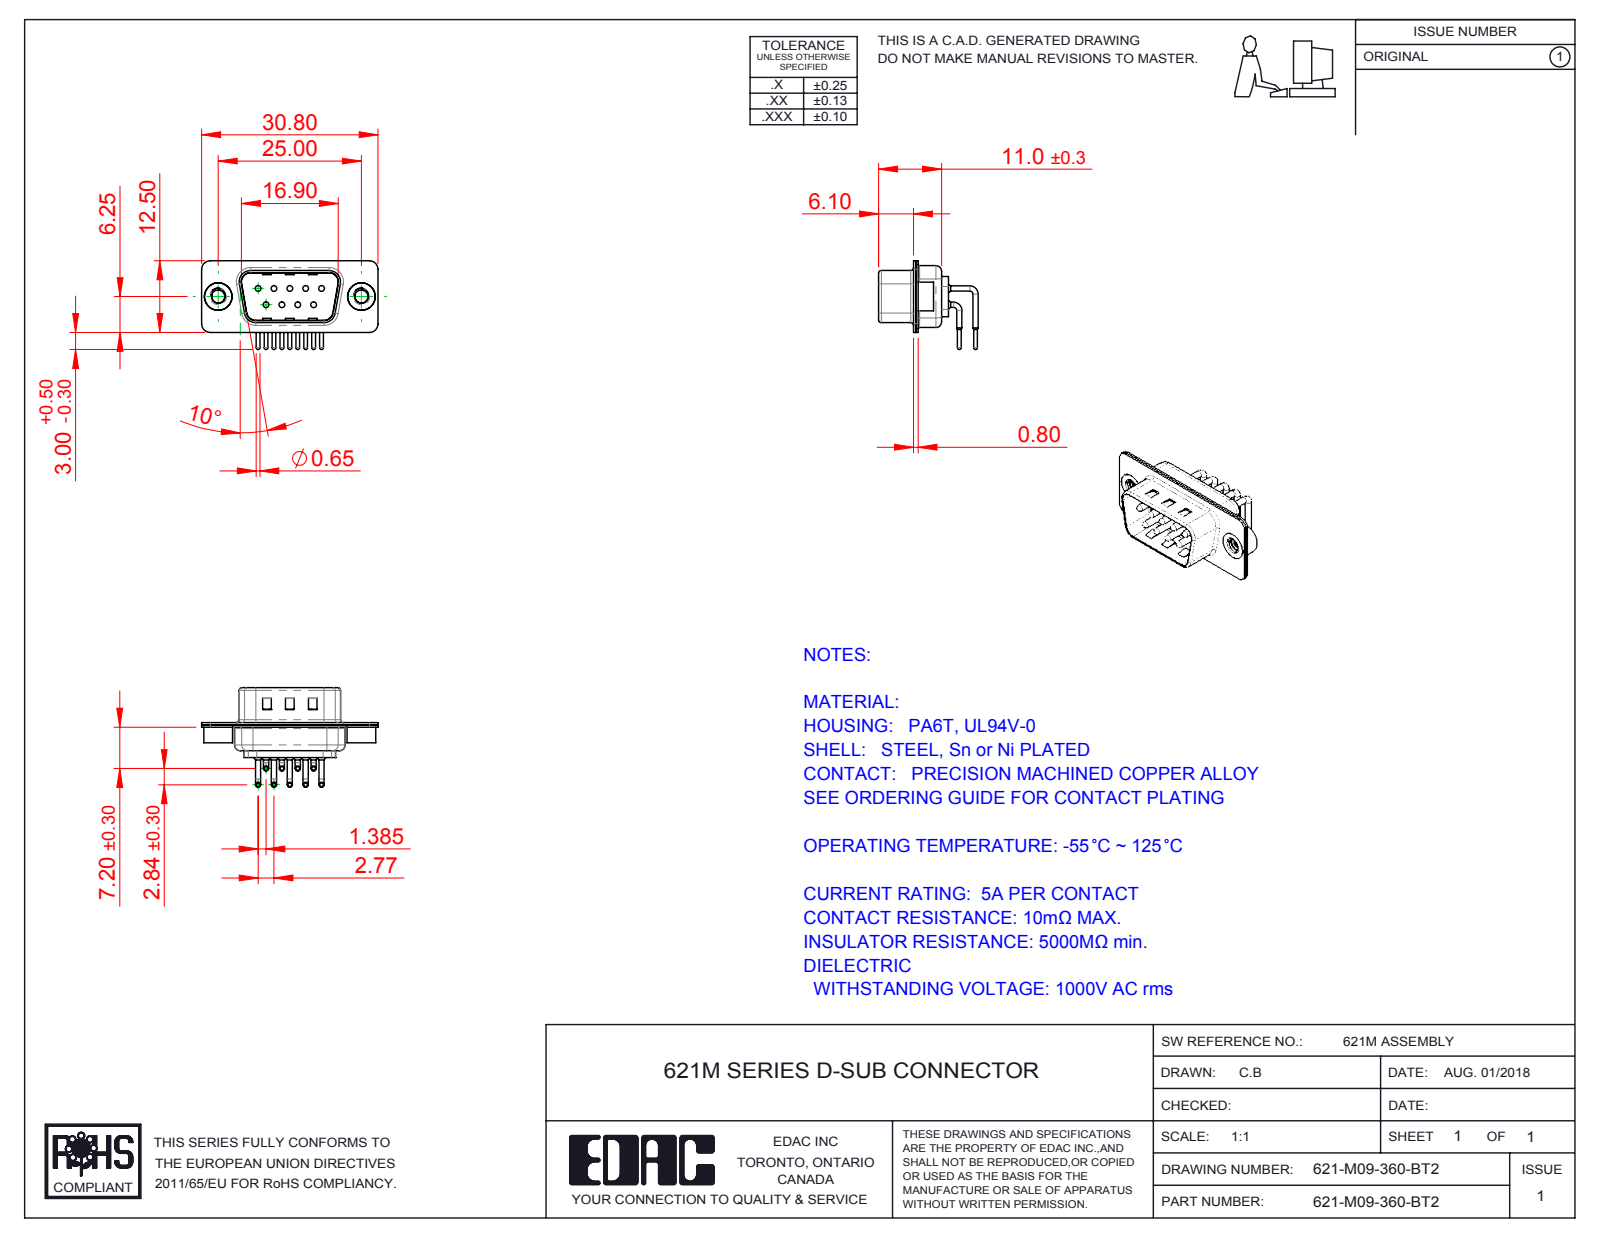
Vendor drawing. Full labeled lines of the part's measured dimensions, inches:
Part name (STEP PRODUCT): 621M Shell Front_09 Contacts; 621M Housing_09 Contacts; 621M Contact Row 2; 621M Shell Rear_09 Contacts (+3 more)
STEP written by: SolidWorks 2016 (CONFIG_CONTROL_DESIGN)
Units: inches
Bodies: 14 solids, 1294 faces (683 planar, 453 cylindrical, 158 other)
Overall size (bounding box): 1.213 × 0.685 × 0.61
Volume: 0.083 in³ · Surface area: 5.969 in²
Round holes (diameter × count): ⌀0.039 ×9, ⌀0.067 ×9, ⌀0.079 ×9, ⌀0.089 ×2, ⌀0.157 ×2, ⌀0.189 ×2
Round bosses / shafts (diameter × count): ⌀0.035 ×18, ⌀0.059 ×9, ⌀0.026 ×9, ⌀0.197 ×2, ⌀0.193 ×2
Partial cylindrical surfaces — rounded edges, fillets, slot ends (radius × count): R0.059 ×16, R0.079 ×12, R0.04 ×9, R0.02 ×8, R0.063 ×8, R0.01 ×4, R0.024 ×4, R0.026 ×4
Main face-to-face distances: 0.016, 0.033, 0.031, 0.376, 0.049, 0.409, 0.343, 0.014, 0.24, 0.224
Hole centre spacings: 0.124, 0.109, 0.218, 0.198, 0.198, 0.327, 0.28, 0.294
